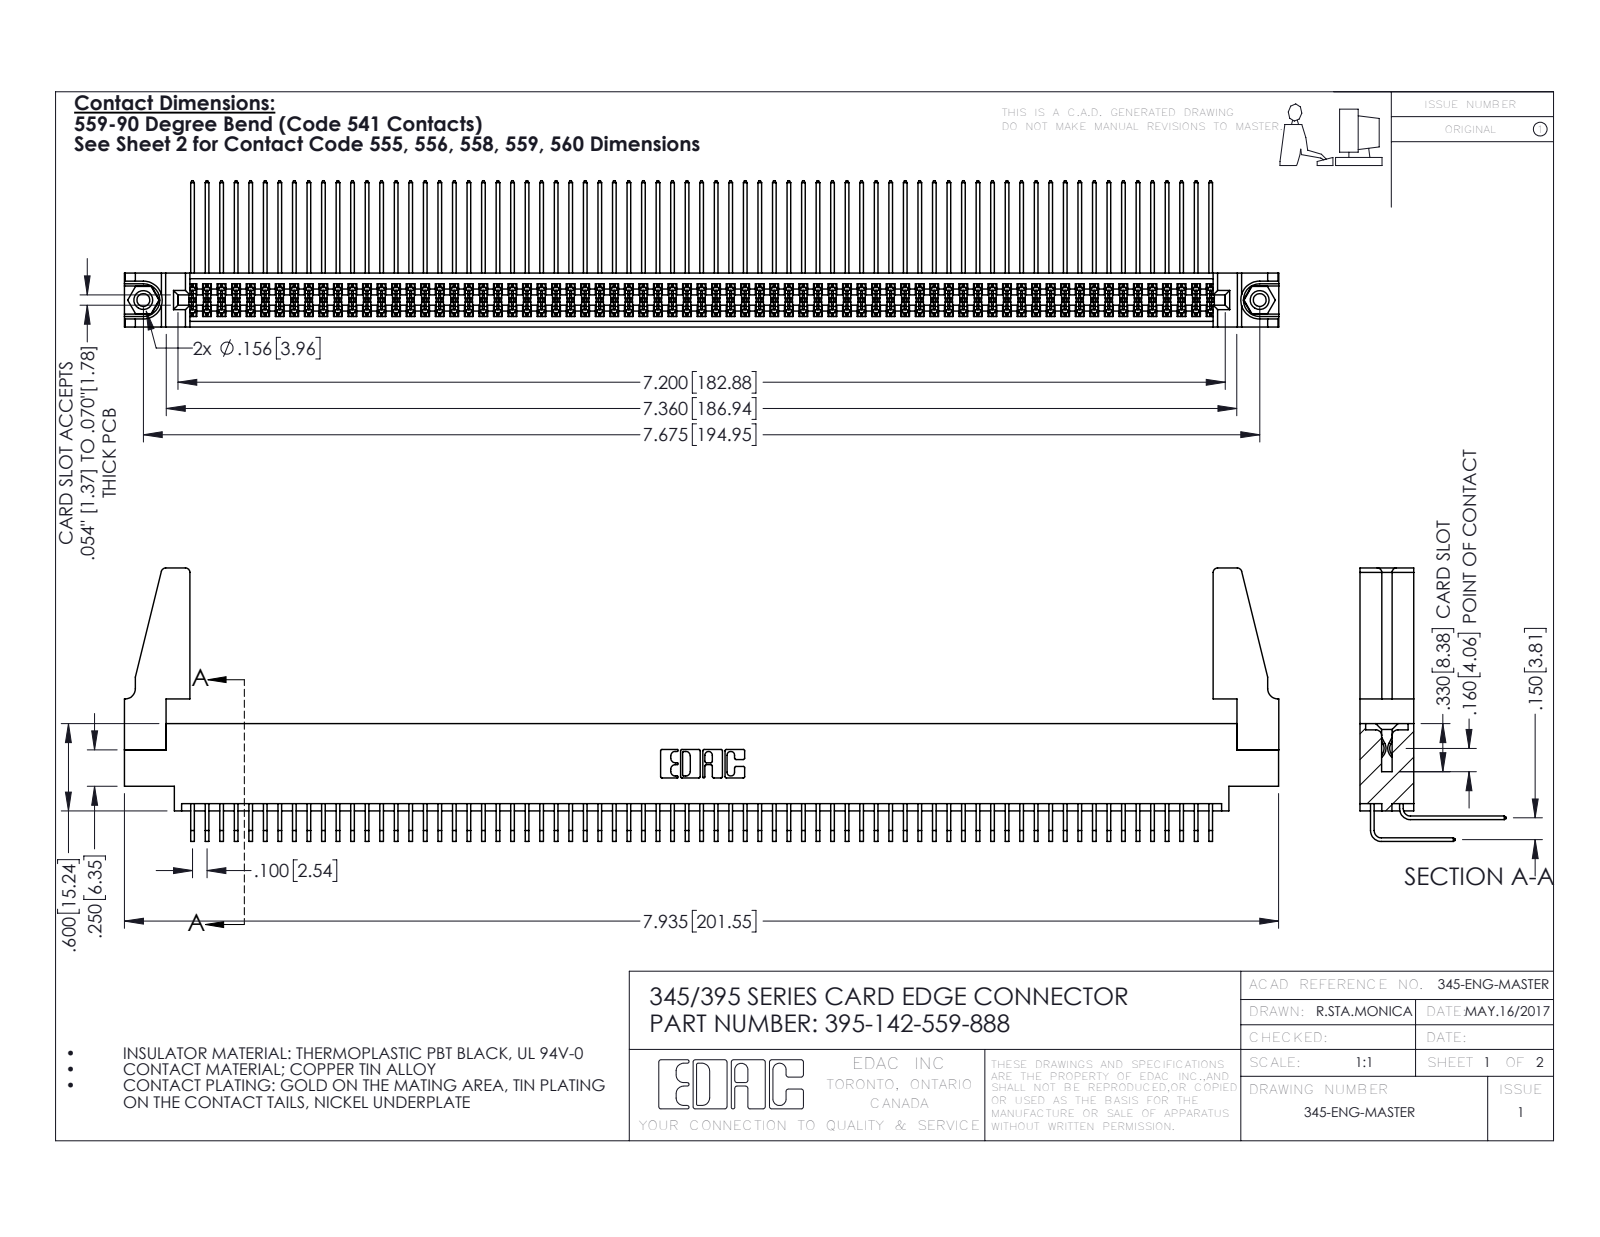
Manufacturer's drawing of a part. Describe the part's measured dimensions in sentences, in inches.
The part is named "345 Part_0.170 Offset - 0.156 Dia-TH; 345-292-001_558 559 Tail - 1; 395-142-559-888; 345-250-001_345-250-001-102 (+2 more)". Its 3-D file was written by "SolidWorks 2016 (CONFIG_CONTROL_DESIGN)". It is 147 solids with 7638 faces: 5126 planar, 2496 cylindrical and 16 other. Overall it measures 7.936 by 1.879 by 1.005 inches. Its volume is 1.453 cubic inches and its surface area 59 square inches. Round holes: 2 of diameter 0.089, 2 of diameter 0.125, 2 of diameter 0.156, 1 of diameter 0.064. Round bosses or shafts: 2 of diameter 0.155. Partial cylindrical surfaces (rounded edges, fillets, slot ends): 284 of radius 0.006, 22 of radius 0.01, 8 of radius 0.03, 6 of radius 0.007, 6 of radius 0.031, 3 of radius 0.026, 2 of radius 0.014, 2 of radius 0.019. The main face-to-face distances are 0.072, 0.298, 0.37, 0.098, 0.272, 0.025, 0.2, 0.225, 0.175, 0.15. The hole center spacings are 0.27, 7.439, 7.675.
